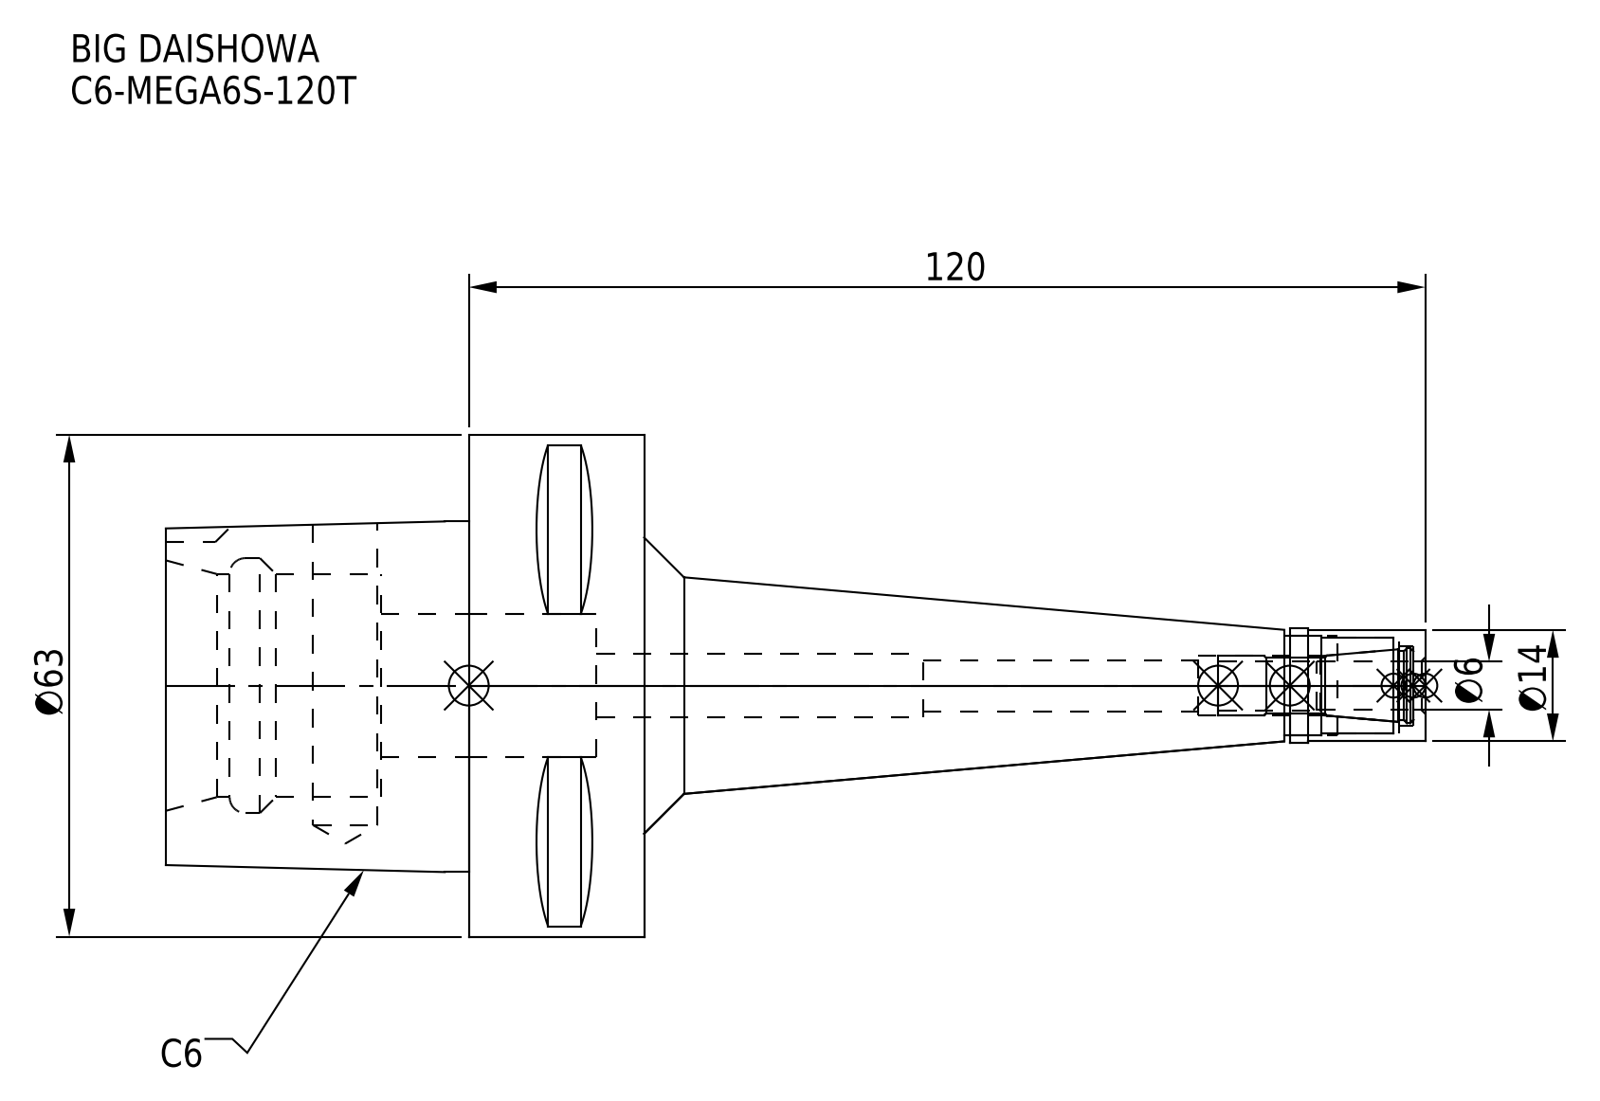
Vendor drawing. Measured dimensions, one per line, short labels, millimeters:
name: C6-MEGA6S-120T_1.stp; C6-MEGA6S-120T-060-FreeParts; C6-MEGA6S-120T-060.stp; C6-MEGA6S-120T-060_ASM.stp (+3 more)
written by: SolidWorks 2019 (CONFIG_CONTROL_DESIGN)
unit: mm
bodies: 2 solids, 93 faces (38 planar, 37 cylindrical, 18 other)
size: 158 × 63 × 63
volume: 124 722 mm³; area: 29 189 mm²
holes: 1× ⌀6.1, 1× ⌀6.4, 1× ⌀7.4, 1× ⌀8, 1× ⌀8.1, 1× ⌀10, 1× ⌀12, 1× ⌀12.5, 1× ⌀18, 1× ⌀28, 1× ⌀32
bosses: 1× ⌀63, 1× ⌀14.3, 1× ⌀14
rounds: 1× R5
face distances: 22, 27, 60, 38, 11, 33, 24.89, 55.4, 6, 16
